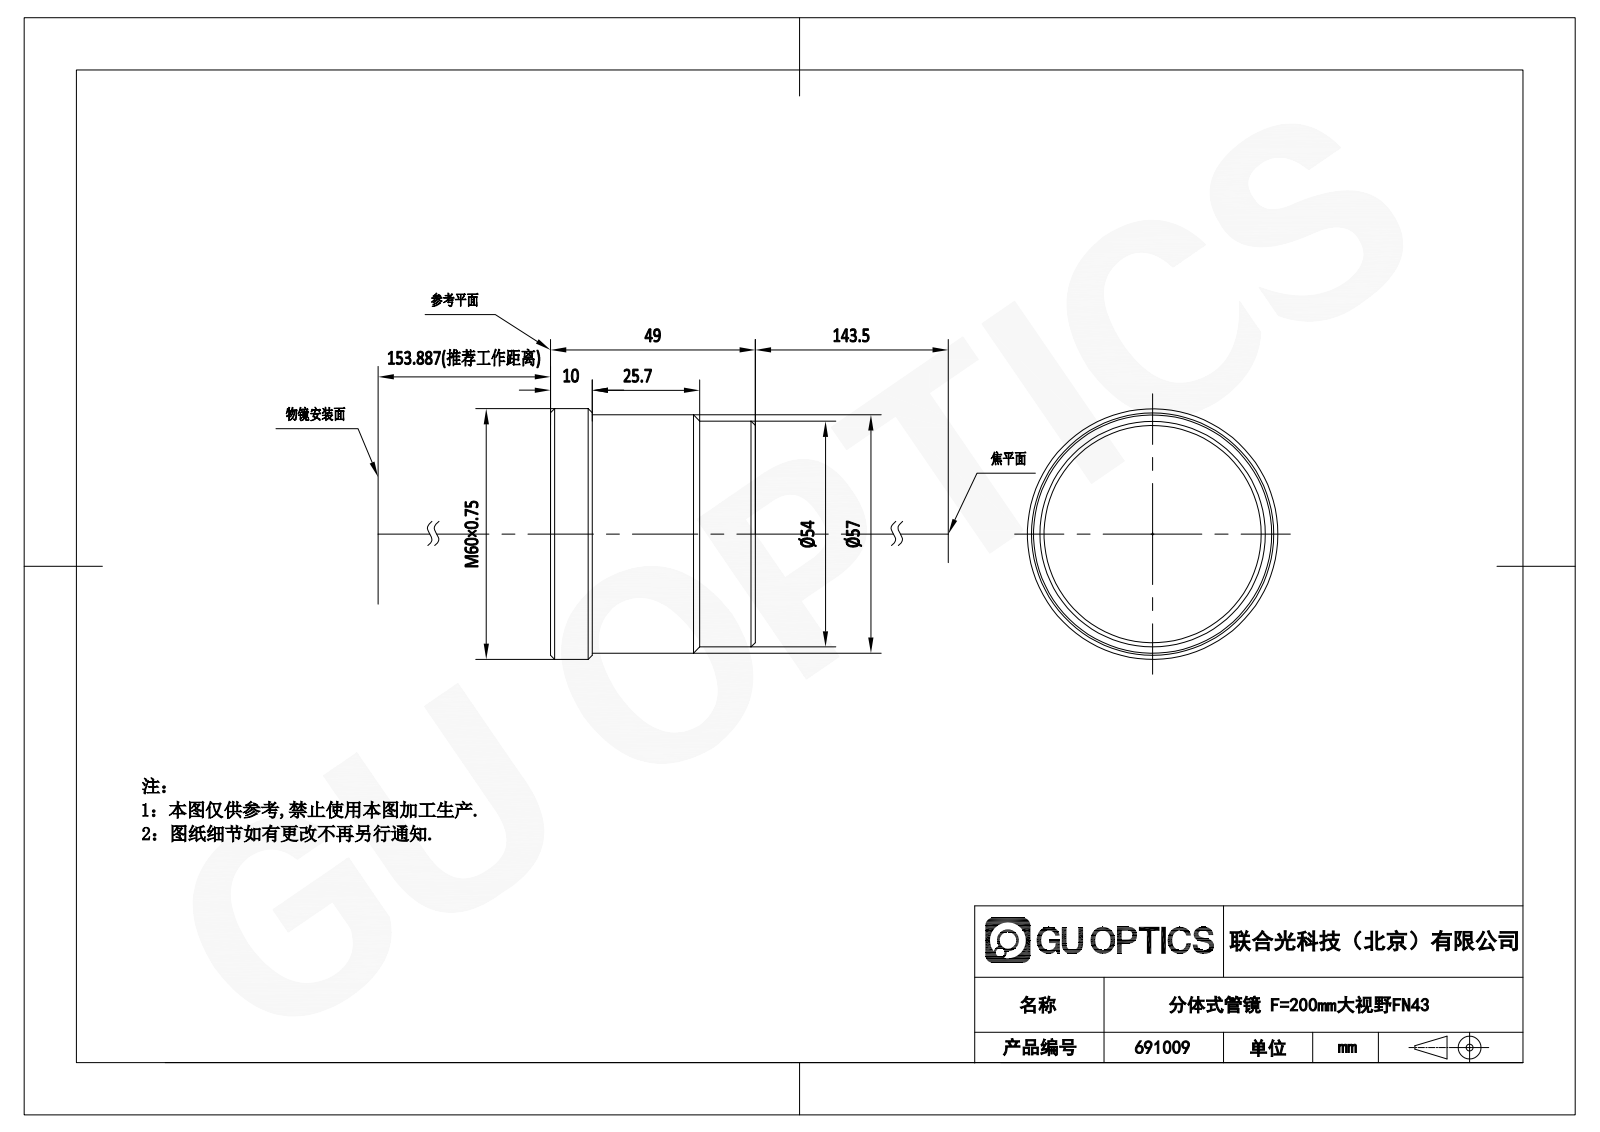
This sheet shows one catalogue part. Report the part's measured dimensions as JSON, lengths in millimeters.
{"part_name": "691009-1", "step_written_by": "SolidWorks 2020 (AUTOMOTIVE_DESIGN)", "units": "millimeters", "bodies": {"solids": 1, "faces": 17, "planar": 3, "cylindrical": 6, "other": 8}, "overall_size": [60, 60, 49], "volume_mm3": 123846, "surface_area_mm2": 13914, "round_bosses_or_shafts": [[60, 1], [57, 1], [54, 1]], "face_to_face_distances": [49, 10, 39]}
